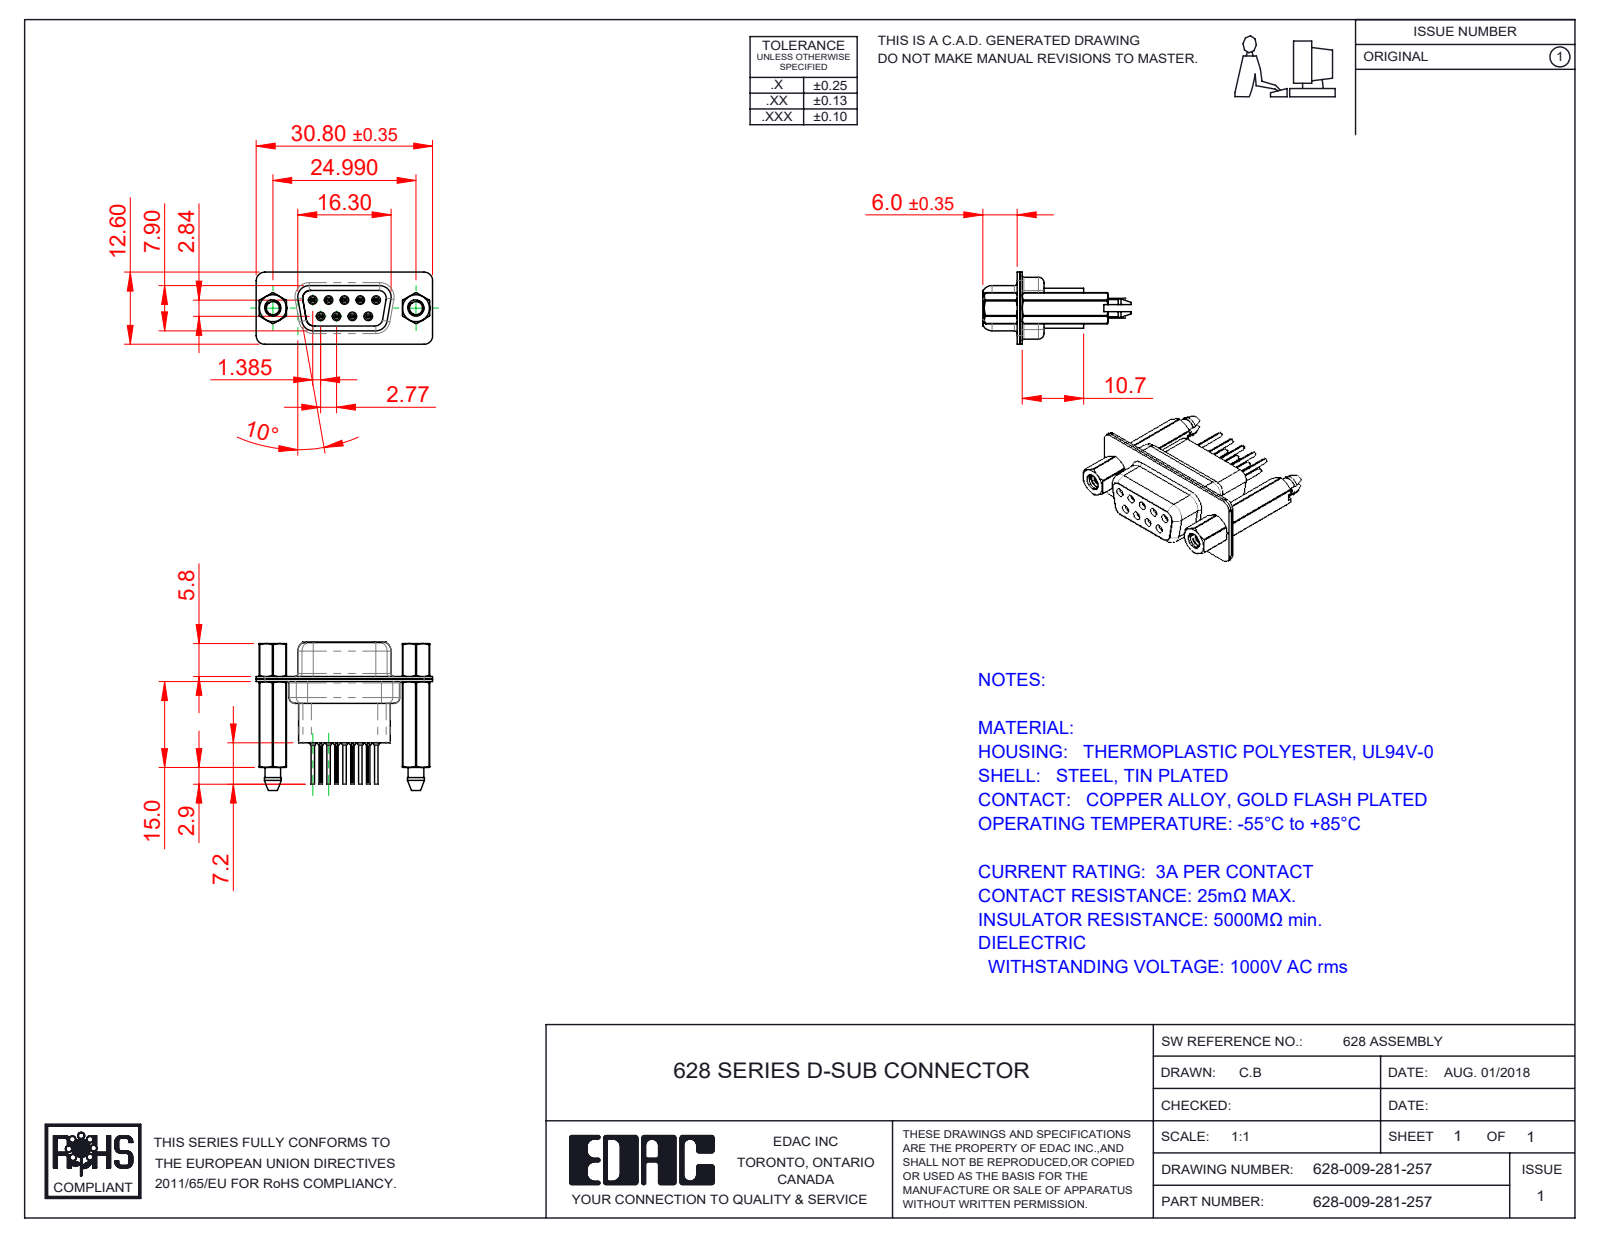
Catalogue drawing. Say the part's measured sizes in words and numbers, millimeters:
The part is named "628 Housing_09 HP; 628 Shell Front_09 Contacts; 628 4-40 Hex Standoff; 628 Contact Row 1_71 (+4 more)". Its 3-D file was written by "SolidWorks 2020 (CONFIG_CONTROL_DESIGN)". It is 16 solids with 1586 faces: 400 planar, 538 cylindrical and 648 other. Overall it measures 30.8 by 25.9 by 12.6 millimeters. Its volume is 2 847 cubic millimeters and its surface area 6 606 square millimeters. Round holes: 9 of diameter 0.2, 9 of diameter 0.8, 9 of diameter 0.9, 9 of diameter 1.1, 9 of diameter 1.6, 5 of diameter 1.7, 2 of diameter 2.26, 2 of diameter 2.29, 2 of diameter 4, 2 of diameter 4.05, 2 of diameter 4.85. Round bosses or shafts: 9 of diameter 2, 9 of diameter 1.5, 9 of diameter 1.2, 9 of diameter 0.6, 2 of diameter 4.95, 2 of diameter 4.8, 2 of diameter 2.79. Partial cylindrical surfaces (rounded edges, fillets, slot ends): 19 of radius 1.5, 18 of radius 0.1, 12 of radius 2, 9 of radius 0.28, 6 of radius 1.35, 6 of radius 1.6, 4 of radius 0.25, 4 of radius 0.5. The main face-to-face distances are 0.45, 0.4, 0.9, 4.76, 8.5, 6.6, 1.9, 1.4, 7, 0.5. The hole center spacings are 3.16, 2.77, 5.54, 5.03, 5.04, 8.31, 7.48, 7.49.
